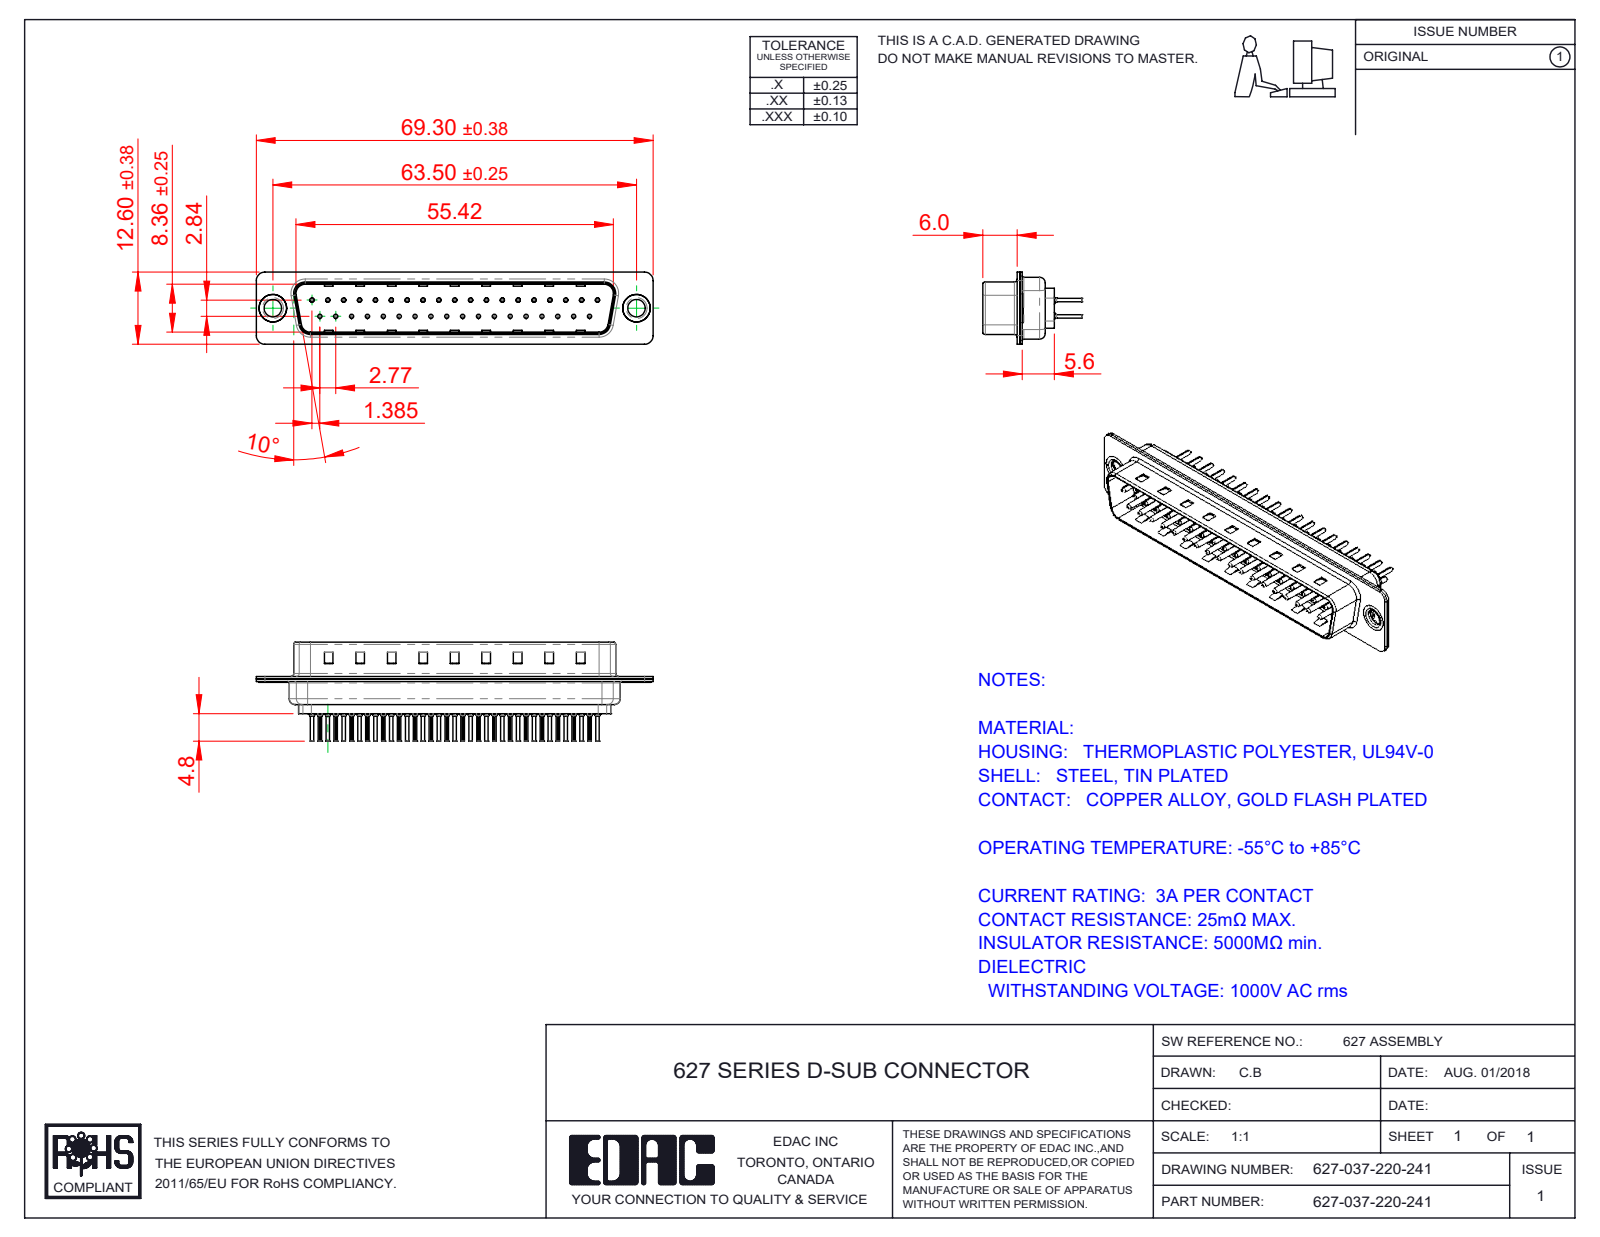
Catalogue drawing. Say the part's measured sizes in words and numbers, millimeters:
The part is named "627 Housing_37 LP; 627 Contact Row 1_20L; 627 Shell Front_37 Contacts; 627 Contact Row 2_20L (+3 more)". Its 3-D file was written by "SolidWorks 2020 (CONFIG_CONTROL_DESIGN)". It is 42 solids with 4012 faces: 1091 planar, 1494 cylindrical and 1427 other. Overall it measures 69.3 by 17.3 by 12.6 millimeters. Its volume is 3 624 cubic millimeters and its surface area 10 536 square millimeters. Round holes: 37 of diameter 0.2, 37 of diameter 0.35, 37 of diameter 1.1, 37 of diameter 1.6, 2 of diameter 3.05, 2 of diameter 4, 2 of diameter 4.8. Round bosses or shafts: 37 of diameter 2, 37 of diameter 1.5, 37 of diameter 0.75, 37 of diameter 0.6, 2 of diameter 5, 2 of diameter 4.9, 2 of diameter 3.55. Partial cylindrical surfaces (rounded edges, fillets, slot ends): 74 of radius 0.1, 16 of radius 1.5, 12 of radius 2, 8 of radius 0.5, 8 of radius 1.6, 4 of radius 0.25, 4 of radius 0.6, 4 of radius 0.65. The main face-to-face distances are 0.4, 0.82, 9.58, 0.45, 8.76, 1.5, 0.9, 1.4, 6.05, 0.5. The hole center spacings are 3.16, 2.77, 5.54, 8.31, 5.04, 10.1, 11.08, 12.78.
